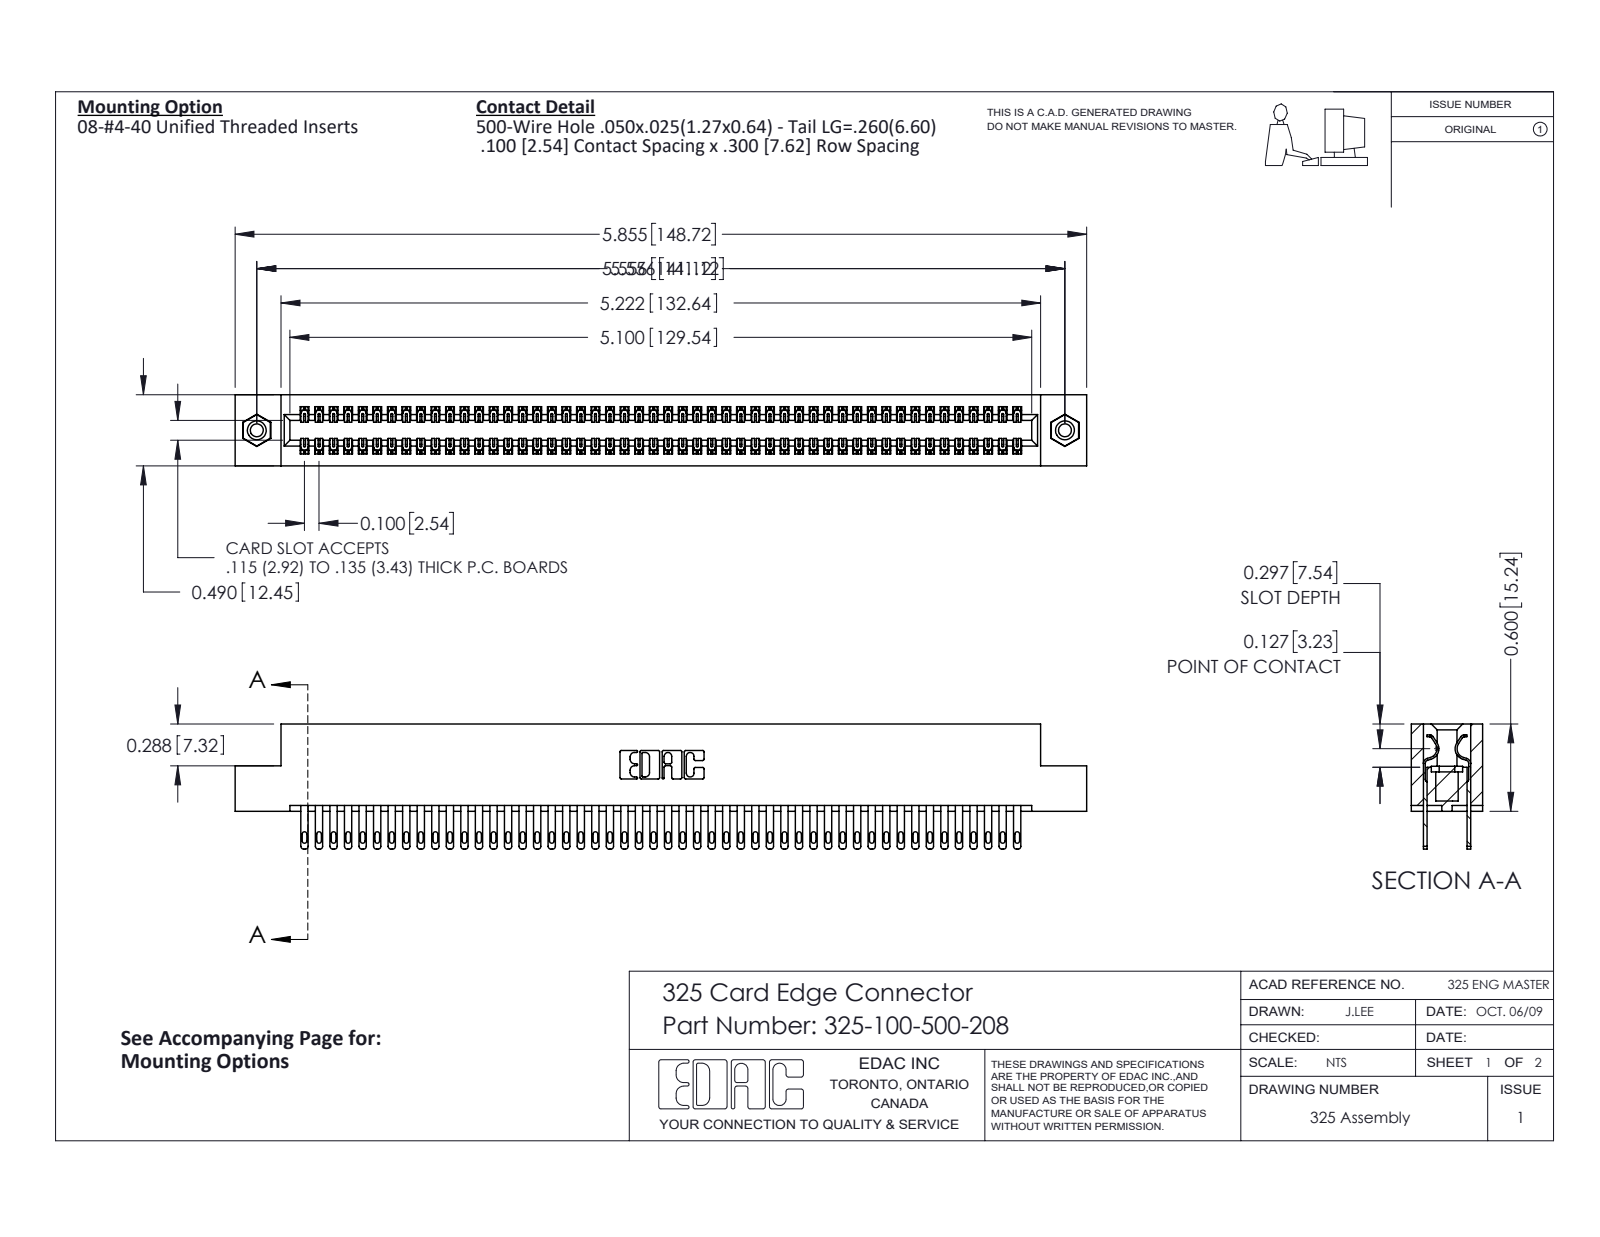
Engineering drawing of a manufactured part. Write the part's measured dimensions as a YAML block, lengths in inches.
part_name: "345-250-001_345-250-003-102; 325-292-001_325-293-100; 325-100-500-208; 325 Part_TI"
step_written_by: "SolidWorks 2016 (CONFIG_CONTROL_DESIGN)"
units: inches
bodies: {solids: 103, faces: 4974, planar: 3102, cylindrical: 1856, other: 16}
overall_size: [5.855, 0.86, 0.49]
volume: 1.194
surface_area: 38.65
round_holes:
  - {diameter: 0.089, count: 2}
  - {diameter: 0.125, count: 2}
  - {diameter: 0.16, count: 2}
round_bosses_or_shafts:
  - {diameter: 0.155, count: 2}
partial_cylinders:
  - {radius: 0.006, count: 150}
  - {radius: 0.016, count: 100}
  - {radius: 0.02, count: 100}
  - {radius: 0.01, count: 22}
  - {radius: 0.007, count: 6}
  - {radius: 0.031, count: 6}
  - {radius: 0.026, count: 3}
  - {radius: 0.014, count: 2}
face_to_face_distances: [0.083, 0.407, 0.3, 0.107, 0.383, 0.025, 0.49, 0.325, 0.275, 0.56]
hole_center_spacings: [5.556]
